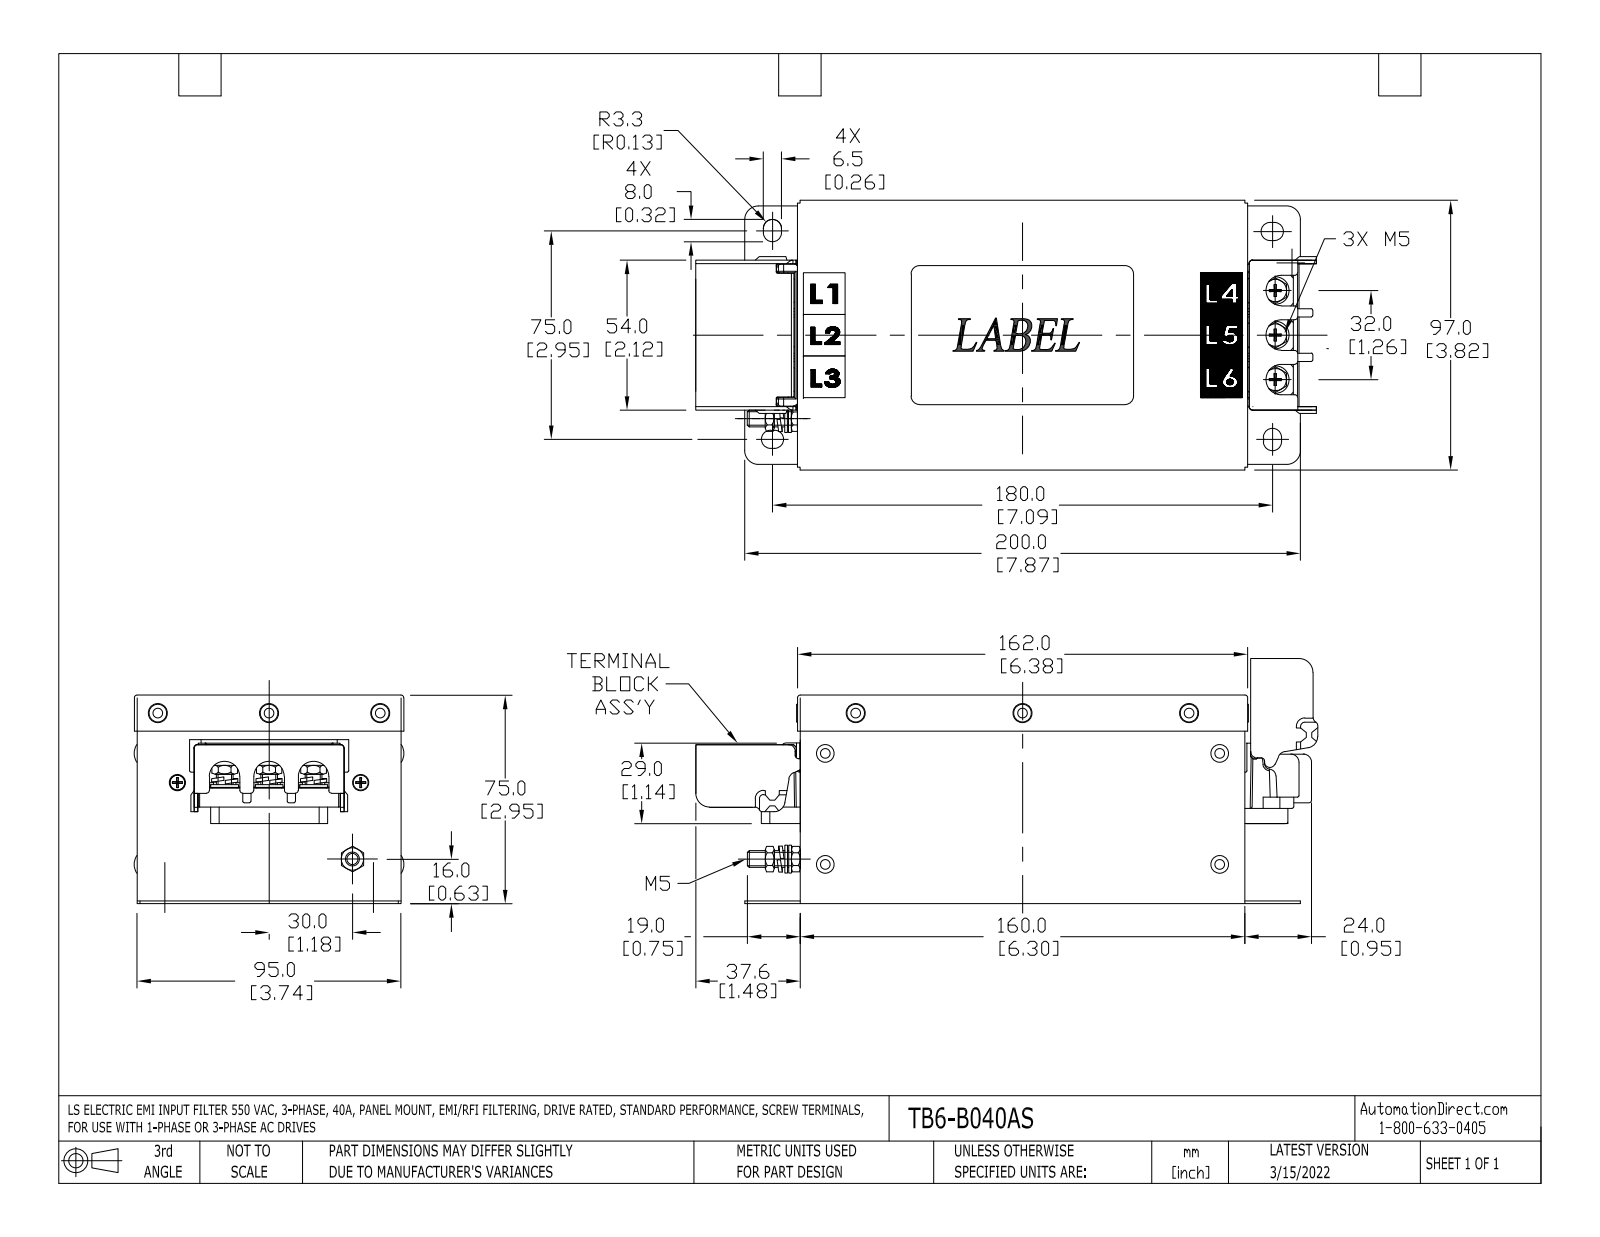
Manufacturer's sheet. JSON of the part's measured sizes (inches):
{"part_name": "TB6-B040AS", "step_written_by": "SolidWorks 2021 (AUTOMOTIVE_DESIGN)", "units": "inches", "bodies": {"solids": 47, "faces": 1904, "planar": 881, "cylindrical": 540, "other": 483}, "overall_size": [8.947, 3.898, 3.828], "volume_in3": 18.74, "surface_area_in2": 284.6, "round_holes": [[0.079, 14], [0.138, 10], [0.13, 9], [0.214, 6], [0.154, 1], [0.165, 1], [0.197, 1], [0.205, 1]], "round_bosses_or_shafts": [[0.138, 14], [0.36, 6], [0.339, 6], [0.252, 4], [0.054, 2], [0.394, 1], [0.262, 1], [0.234, 1]], "partial_cylinders_radius": [[0.02, 122], [0.01, 30], [0.039, 13], [0.079, 12], [0.067, 7], [0.029, 3], [0.076, 3], [0.276, 2]], "face_to_face_distances": [0.047, 3.693, 2.953, 2.906, 2.441, 2.394, 0.512, 6.252, 0.039, 3.646], "hole_center_spacings": [0.394, 1.557, 5.811, 5.824, 7.497, 5.906, 7.47, 0.631]}
